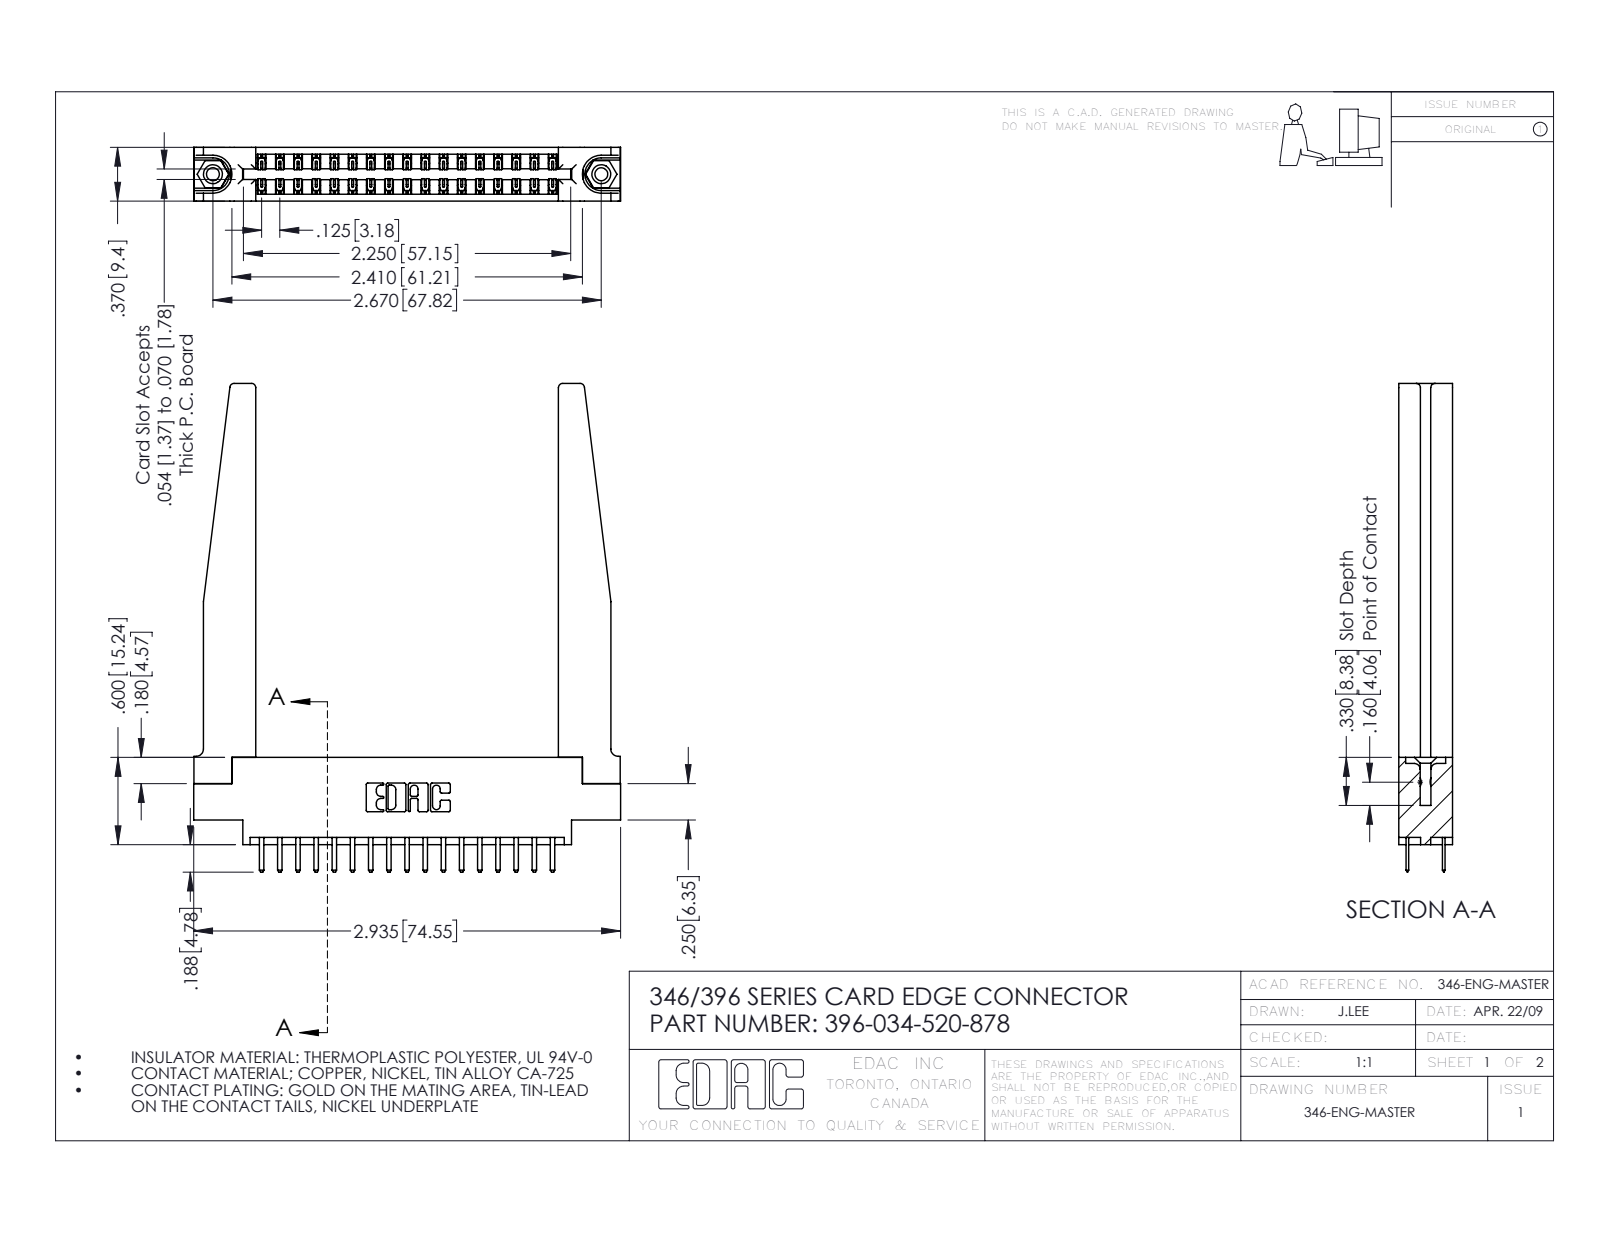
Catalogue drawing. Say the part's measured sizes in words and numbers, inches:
The part is named "346-220-078_345-220-078; 396-034-520-878; 346 Part_0.170 Offset - 0.156 Dia-TH; 345-292-001_345-293-120 (+1 more)". Its 3-D file was written by "SolidWorks 2016 (CONFIG_CONTROL_DESIGN)". It is 39 solids with 2264 faces: 1480 planar, 732 cylindrical and 52 other. Overall it measures 3.358 by 2.935 by 0.37 inches. Its volume is 0.843 cubic inches and its surface area 24.46 square inches. Round holes: 2 of diameter 0.089, 2 of diameter 0.125, 2 of diameter 0.156, 1 of diameter 0.064. Round bosses or shafts: 2 of diameter 0.155. Partial cylindrical surfaces (rounded edges, fillets, slot ends): 51 of radius 0.006, 38 of radius 0.01, 22 of radius 0.01, 8 of radius 0.03, 6 of radius 0.007, 6 of radius 0.031, 3 of radius 0.026, 2 of radius 0.014. The main face-to-face distances are 0.37, 0.15, 0.048, 0.322, 0.072, 0.148, 0.25, 0.102, 0.22, 0.173. The hole center spacings are 0.246, 2.463, 2.67.
